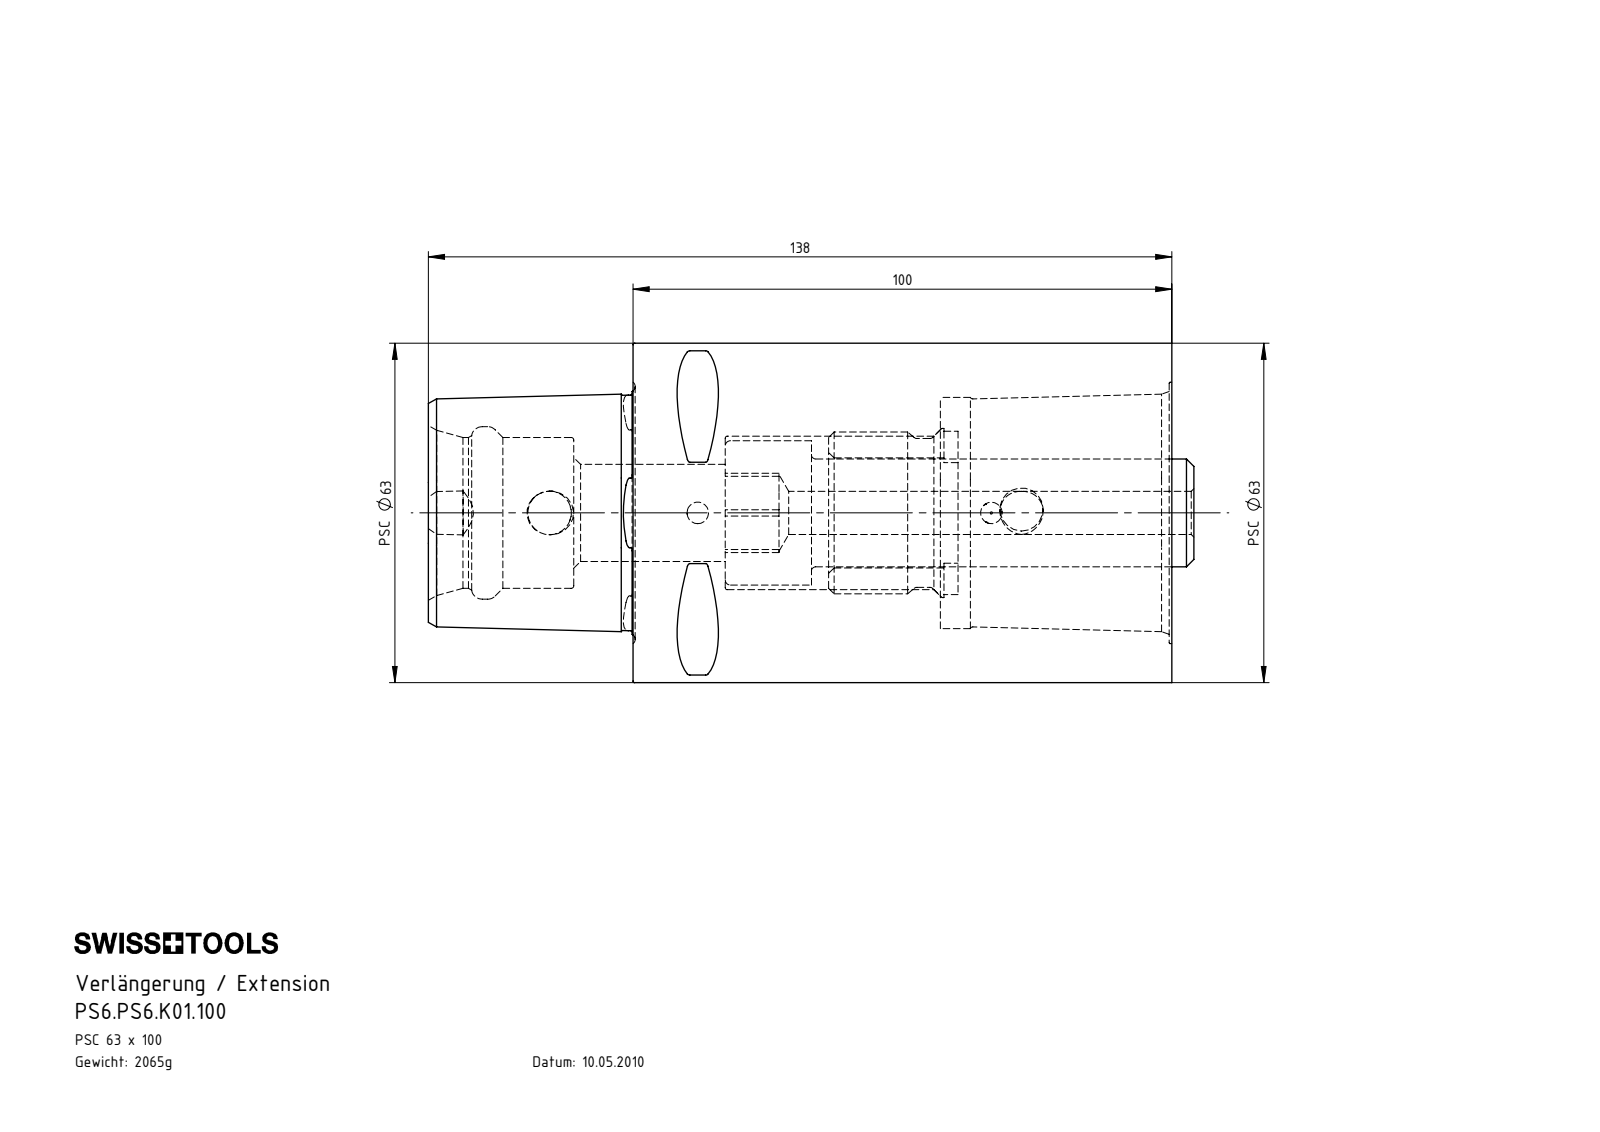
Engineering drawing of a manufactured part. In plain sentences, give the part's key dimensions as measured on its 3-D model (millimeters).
The part is named "PS6.PS6.K01.100; PS6-ER1.K01.071_A; PS6-PS6.K01.100_C; PS6-ER2.001.024_A". Its 3-D file was written by "SolidWorks 2017 (AUTOMOTIVE_DESIGN)". It is 3 solids with 235 faces: 36 planar, 68 cylindrical and 131 other. Overall it measures 141.6 by 63 by 63 millimeters. Its volume is 284 841 cubic millimeters and its surface area 58 232 square millimeters. Round holes: 1 of diameter 4, 1 of diameter 8, 1 of diameter 8.1, 1 of diameter 10, 1 of diameter 18, 1 of diameter 20.4, 1 of diameter 28, 1 of diameter 28.5, 1 of diameter 32, 1 of diameter 48.5. Round bosses or shafts: 1 of diameter 63, 1 of diameter 31.4, 1 of diameter 30, 1 of diameter 27.6, 1 of diameter 27.5, 1 of diameter 20. Partial cylindrical surfaces (rounded edges, fillets, slot ends): 8 of radius 0.5, 7 of radius 6, 6 of radius 2.3, 3 of radius 12.4, 3 of radius 30.5. The main face-to-face distances are 100, 17.1, 82.9, 57.05, 39.95, 42.95, 38, 55.1, 95.05, 138. The hole center spacings are 27.5, 83, 110.5.
